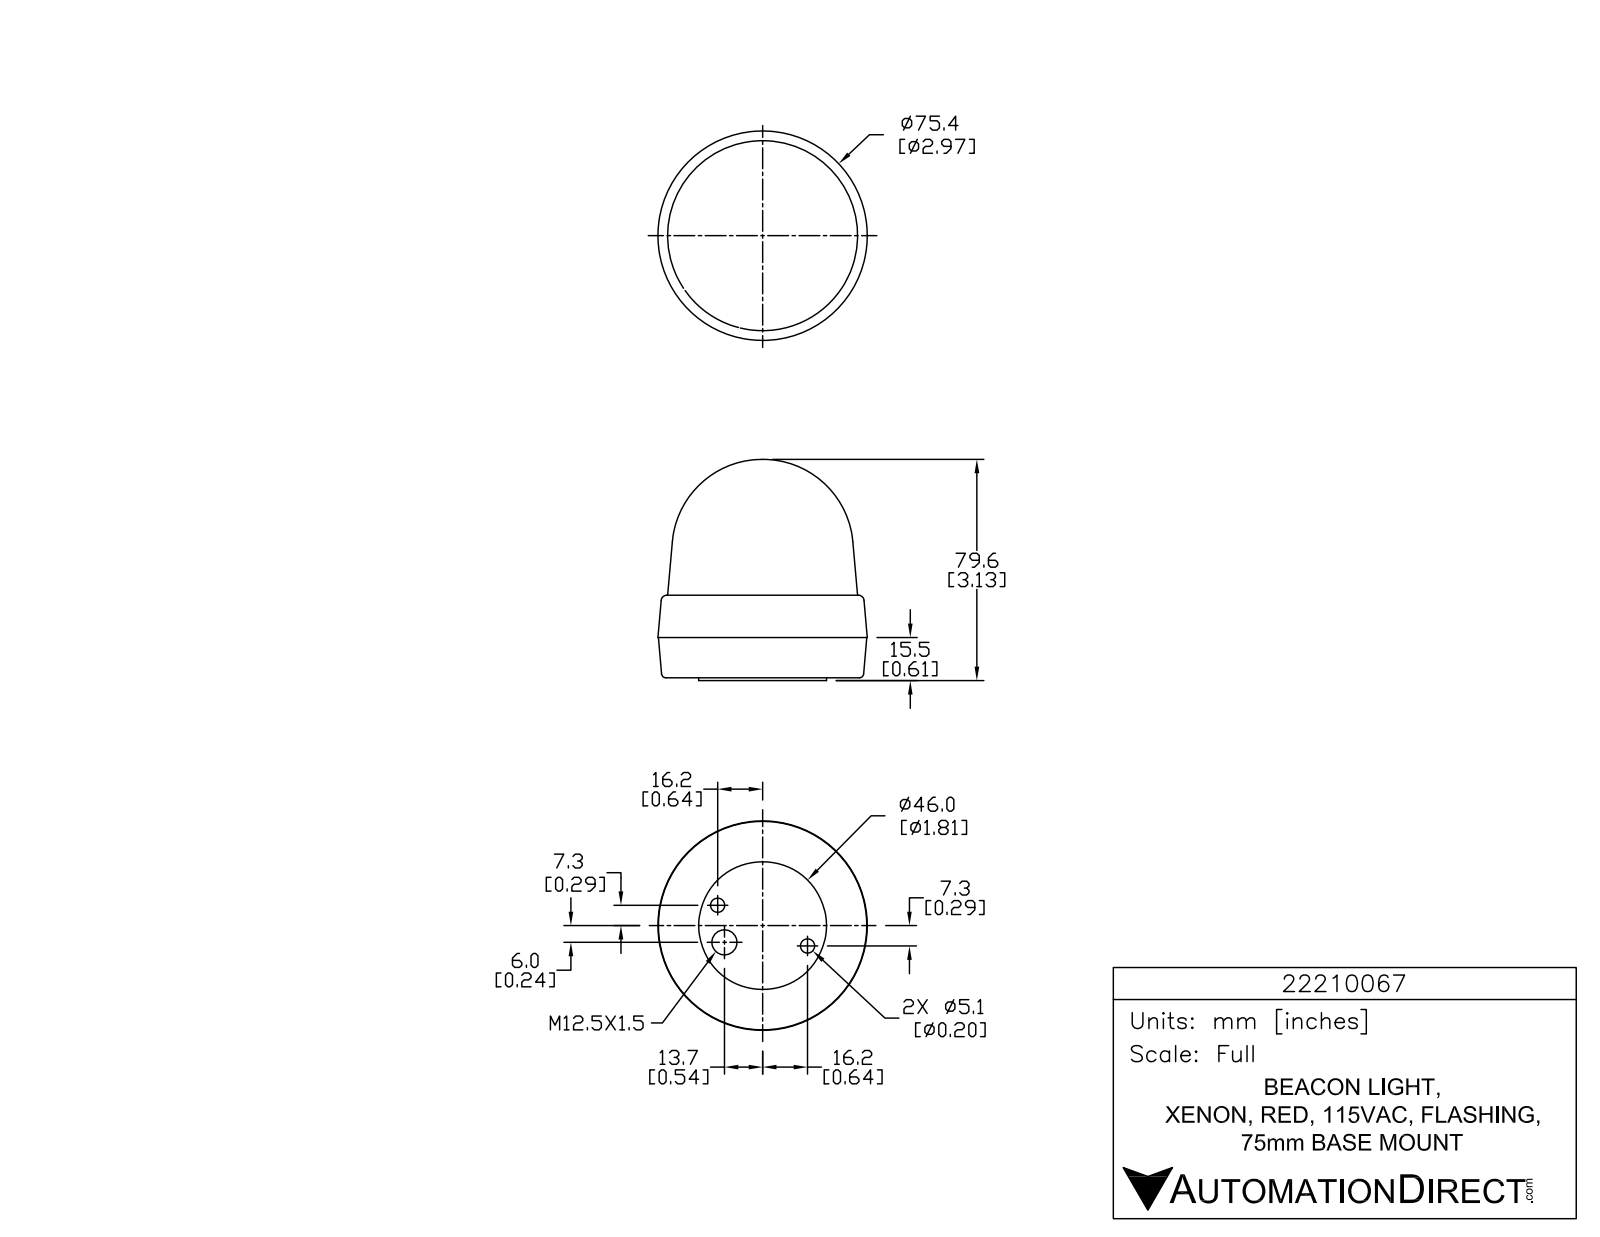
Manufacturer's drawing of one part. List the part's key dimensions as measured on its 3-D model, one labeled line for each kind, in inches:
Part name (STEP PRODUCT): 22210067
STEP written by: SolidWorks 2015 (AUTOMOTIVE_DESIGN)
Units: inches
Bodies: 1 solid, 773 faces (526 planar, 163 cylindrical, 84 other)
Overall size (bounding box): 3.133 × 2.967 × 2.967
Volume: 15.79 in³ · Surface area: 33.7 in²
Round holes (diameter × count): ⌀0.059 ×3, ⌀0.201 ×2, ⌀0.354 ×1
Round bosses / shafts (diameter × count): ⌀0.339 ×3, ⌀0.084 ×3, ⌀1.811 ×1
Partial cylindrical surfaces — rounded edges, fillets, slot ends (radius × count): R0.005 ×9, R0.005 ×6, R0.012 ×6, R0.012 ×6, R0.012 ×6, R0.196 ×6, R0.005 ×3, R0.005 ×3
Main face-to-face distances: 0.039, 1.209, 1.17, 0.61, 0.571, 0.599, 1.566, 1.527, 0.956, 0.357
Hole centre spacings: 0.534, 1.179, 1.398
